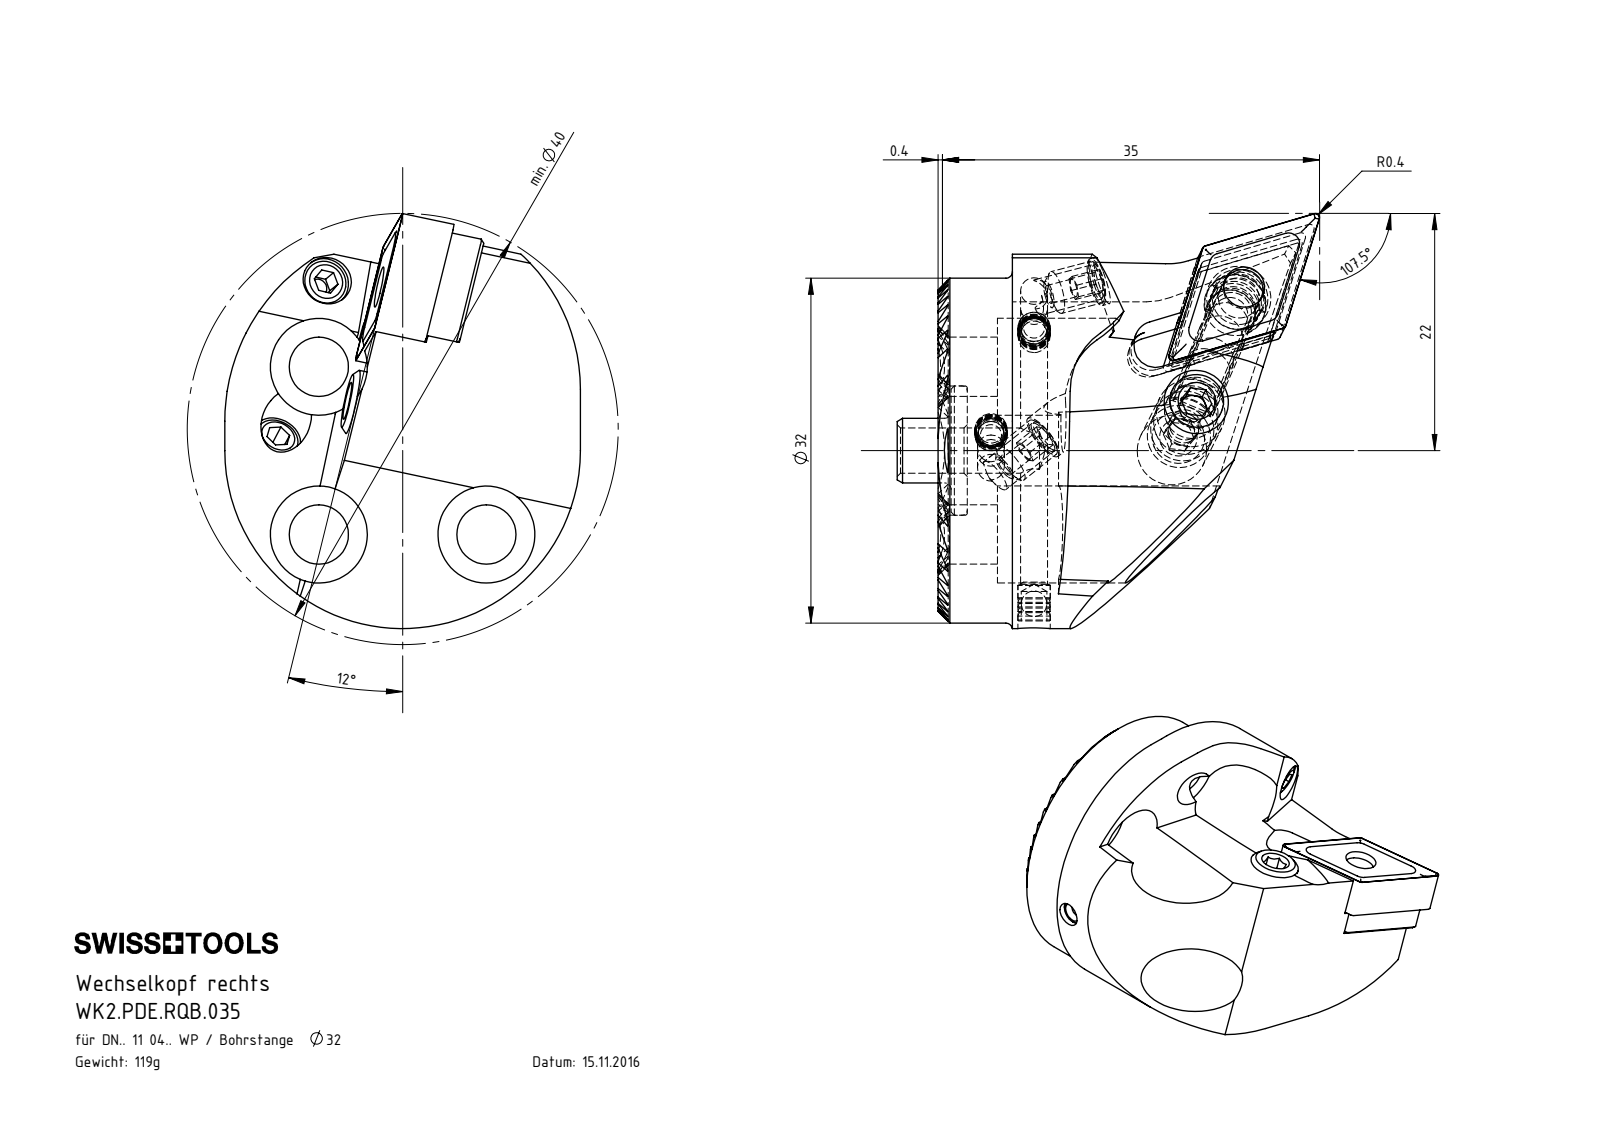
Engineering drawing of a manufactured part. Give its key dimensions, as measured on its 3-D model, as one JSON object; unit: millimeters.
{"part_name": "WK2-PDE.RQB.035_A; WDE-ER2.101.003_A; DNMG110404; WK2.PDE.RQB.035 (+6 more)", "step_written_by": "SolidWorks 2017 (AUTOMOTIVE_DESIGN)", "units": "millimeters", "bodies": {"solids": 15, "faces": 481, "planar": 258, "cylindrical": 112, "other": 111}, "overall_size": [39.21, 38.5, 33], "volume_mm3": 15554, "surface_area_mm2": 9659, "round_holes": [[2.38, 3], [2.5, 3], [5.5, 3], [9, 3], [1.7, 2], [3, 2], [3.3, 2], [4.5, 2], [3.81, 1], [4.2, 1], [4.8, 1], [5, 1]], "round_bosses_or_shafts": [[3, 3], [6, 2], [4, 2], [32, 1], [12, 1], [5.9, 1], [2.87, 1]], "partial_cylinders_radius": [[0.12, 22], [0.4, 8], [2.1, 5], [7, 2], [1.83, 1], [1.85, 1], [2.25, 1], [2.35, 1]], "face_to_face_distances": [1.3, 2.6, 3.9, 5.2, 6.5, 7.8, 12.99, 11.69, 14.29, 10.39], "hole_center_spacings": [11, 11.8, 15.56, 22.01]}
